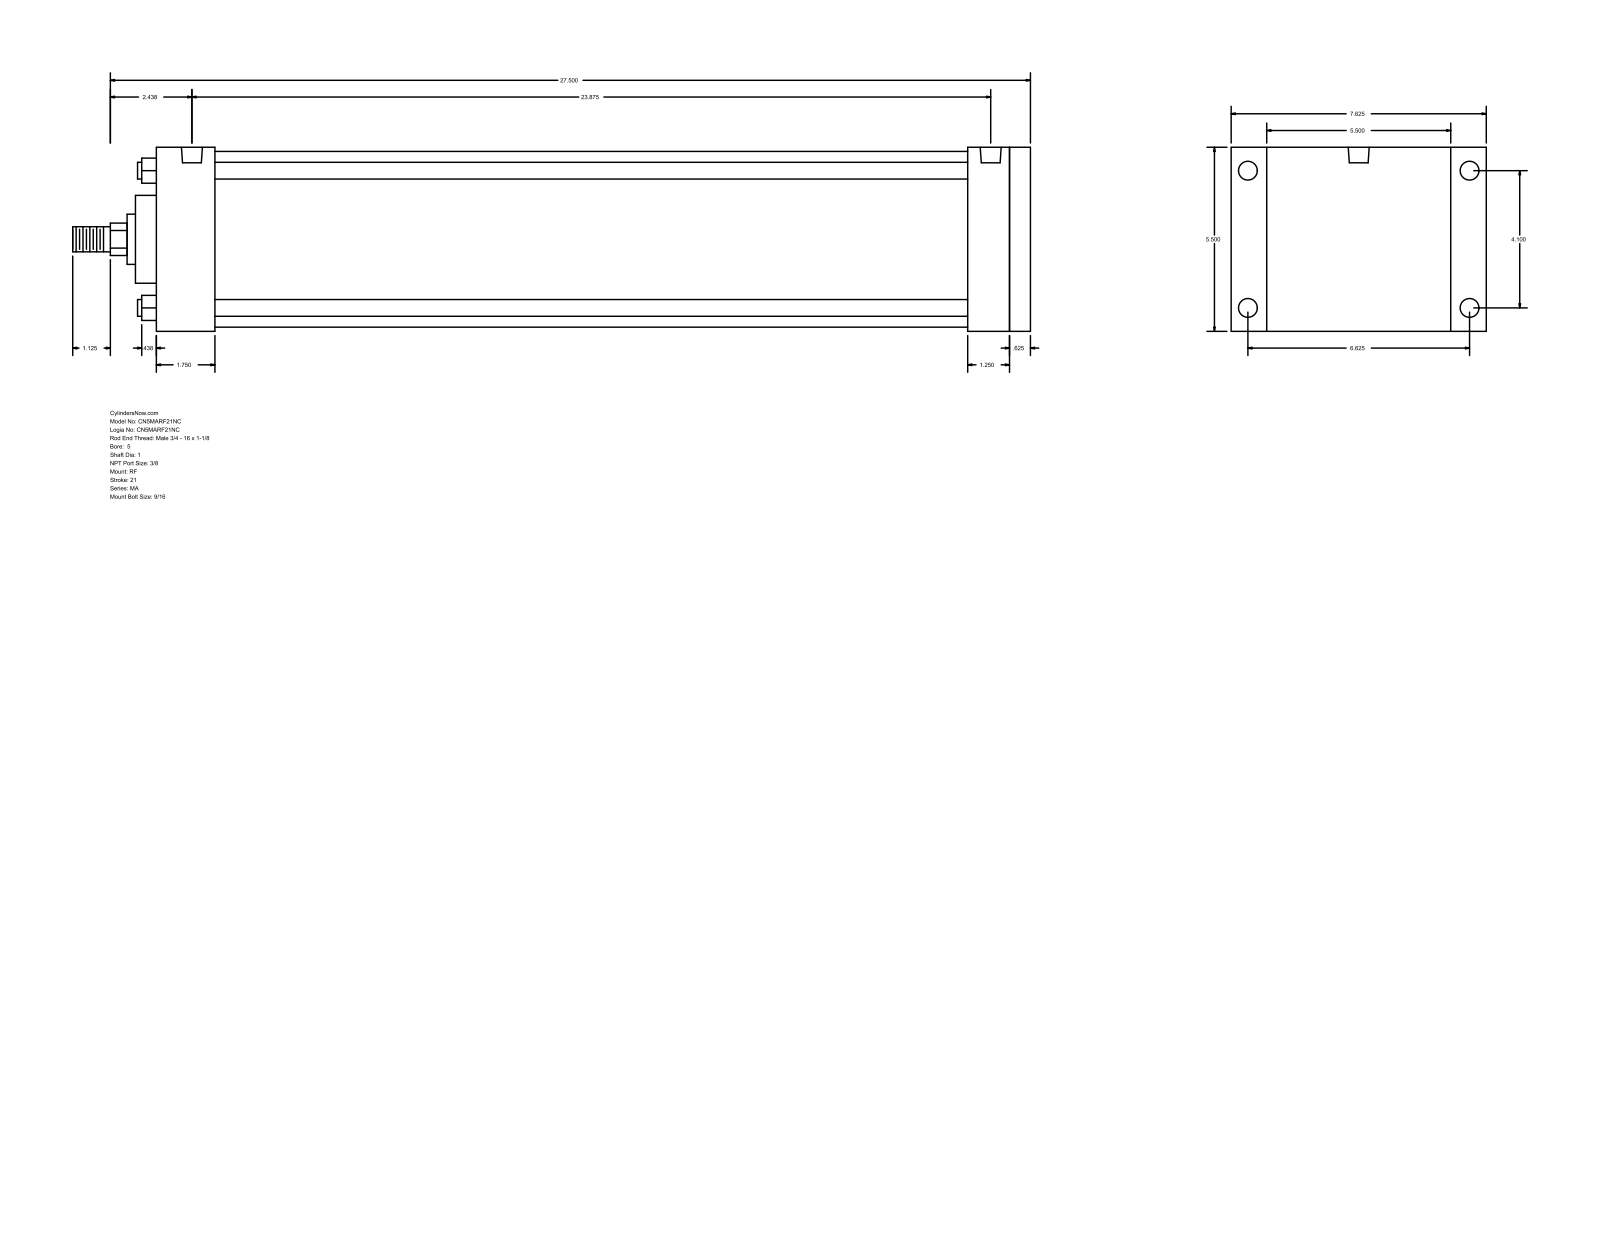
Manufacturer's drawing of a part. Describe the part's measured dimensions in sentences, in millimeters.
The part is named "MA_RF__0500_1". Its 3-D file was written by "GSSL Pune (CONFIG_CONTROL_DESIGN)". It is 0 solids with 94 faces: 65 planar, 29 cylindrical and 0 other. Overall it measures 727.08 by 193.68 by 139.7 millimeters. Round holes: 4 of diameter 11.11, 4 of diameter 14.29, 2 of diameter 15.93. Round bosses or shafts: 4 of diameter 12.7, 1 of diameter 133.35, 1 of diameter 66.67, 1 of diameter 38.1, 1 of diameter 25.4, 1 of diameter 19.05. Partial cylindrical surfaces (rounded edges, fillets, slot ends): 1 of radius 12.29. The main face-to-face distances are 139.7, 663.58, 647.7, 15.88, 47.62, 44.46, 603.24, 619.12, 615.96, 571.5. The hole center spacings are 4.76, 104.14, 168.28, 197.9, 596.91, 601.67, 606.43.
